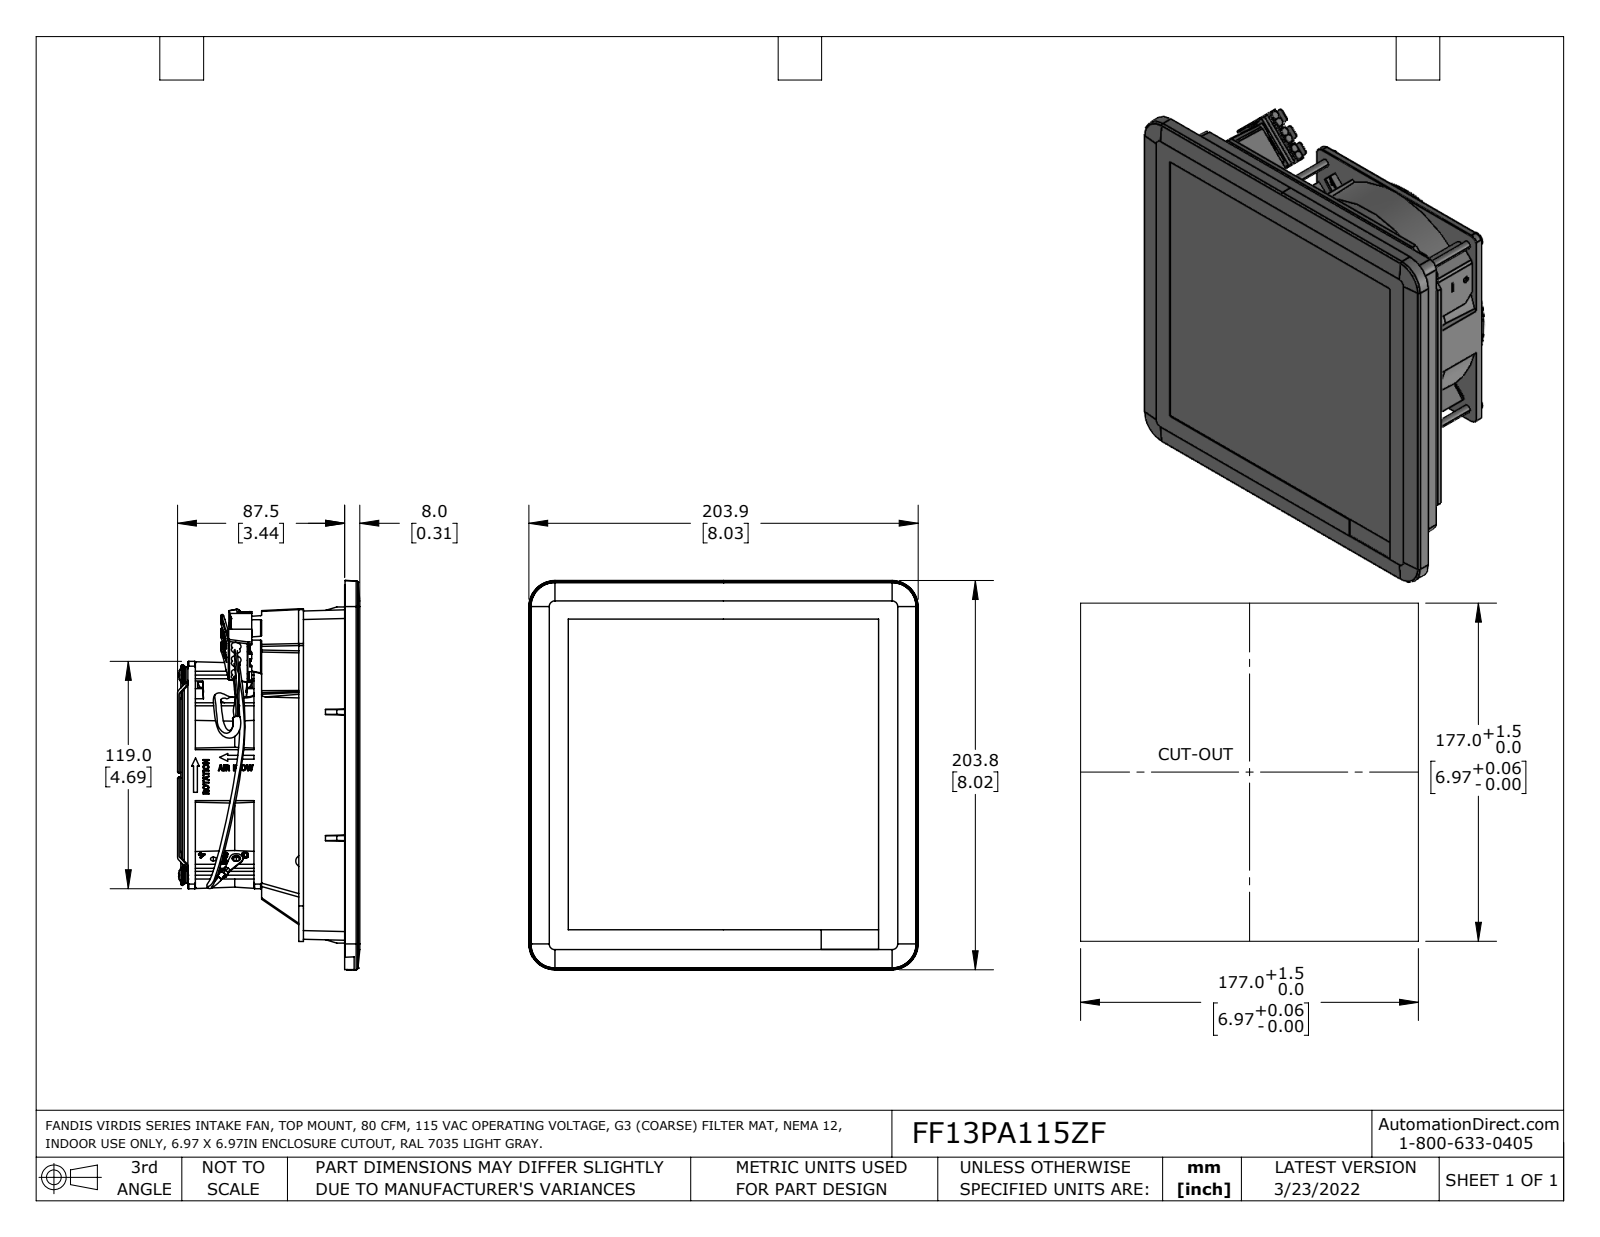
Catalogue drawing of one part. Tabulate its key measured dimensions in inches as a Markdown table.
| quantity | value |
| --- | --- |
| part name | FF13PA115UF |
| STEP written by | SolidWorks 2021 (AUTOMOTIVE_DESIGN) |
| units | inches |
| bodies | 12 solids, 1675 faces (1026 planar, 321 cylindrical, 328 other) |
| overall size | 8.028 × 8.027 × 3.76 |
| volume | 115.7 in³ |
| surface area | 260.3 in² |
| round holes (diameter × count) | 0.169 × 6, 0.118 × 4, 0.138 × 2, 0.173 × 1 |
| round bosses / shafts (diameter × count) | 0.315 × 4, 0.157 × 4, 0.039 × 1 |
| partial cylindrical surfaces (radius × count) | 0.012 × 42, 0.02 × 32, 0.059 × 18, 0.177 × 14, 0.016 × 13, 0.028 × 13, 0.024 × 9, 0.118 × 8 |
| main face-to-face distances | 3.528, 0.295, 3.232, 0.02, 0.315, 3.547, 1.26, 1.24, 0.945, 2.287 |
| hole center spacings | 0.472, 5.137, 4.126, 5.115, 5.115, 5.835, 0.787, 5.137 |
